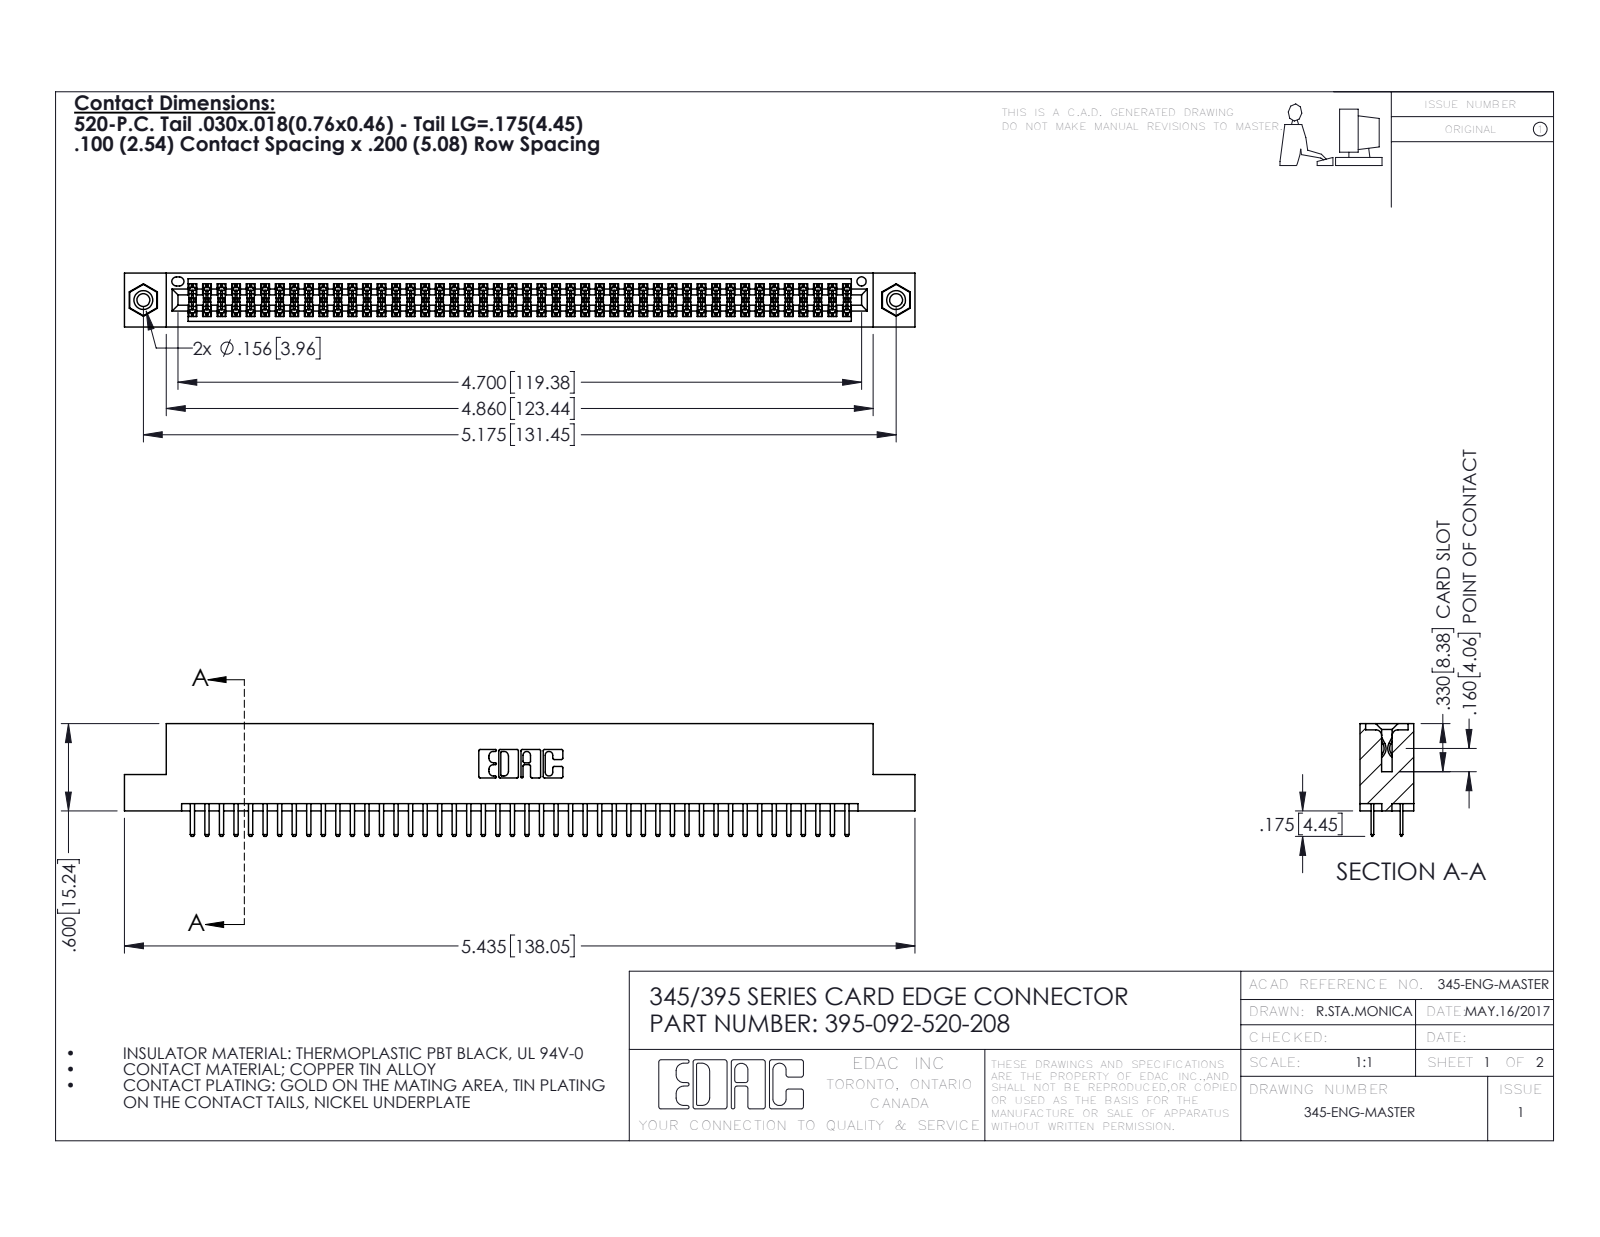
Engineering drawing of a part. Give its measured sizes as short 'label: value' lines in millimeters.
name: 345 Part_Flush Mounting Lugs - 0.156 Dia-TI; 345-250-001_345-250-003-102; 395-092-520-208; 345-292-001_345-293-120
written by: SolidWorks 2016 (CONFIG_CONTROL_DESIGN)
unit: mm
bodies: 95 solids, 5154 faces (3332 planar, 1806 cylindrical, 16 other)
size: 138 × 19.7 × 9.4
volume: 13 400 mm³; area: 19 810 mm²
holes: 2× ⌀2.3, 2× ⌀3.2, 2× ⌀4, 1× ⌀1.6
bosses: 2× ⌀3.9
rounds: 138× R0.2, 96× R0.3, 22× R0.3, 6× R0.2, 6× R0.8, 3× R0.7, 2× R0.4, 2× R0.5
face distances: 1.8, 7.6, 5.1, 9.4, 2.5, 6.9, 0.6, 5.7, 0.6, 1.8
hole spacings: 6.9, 125.5, 131.4
